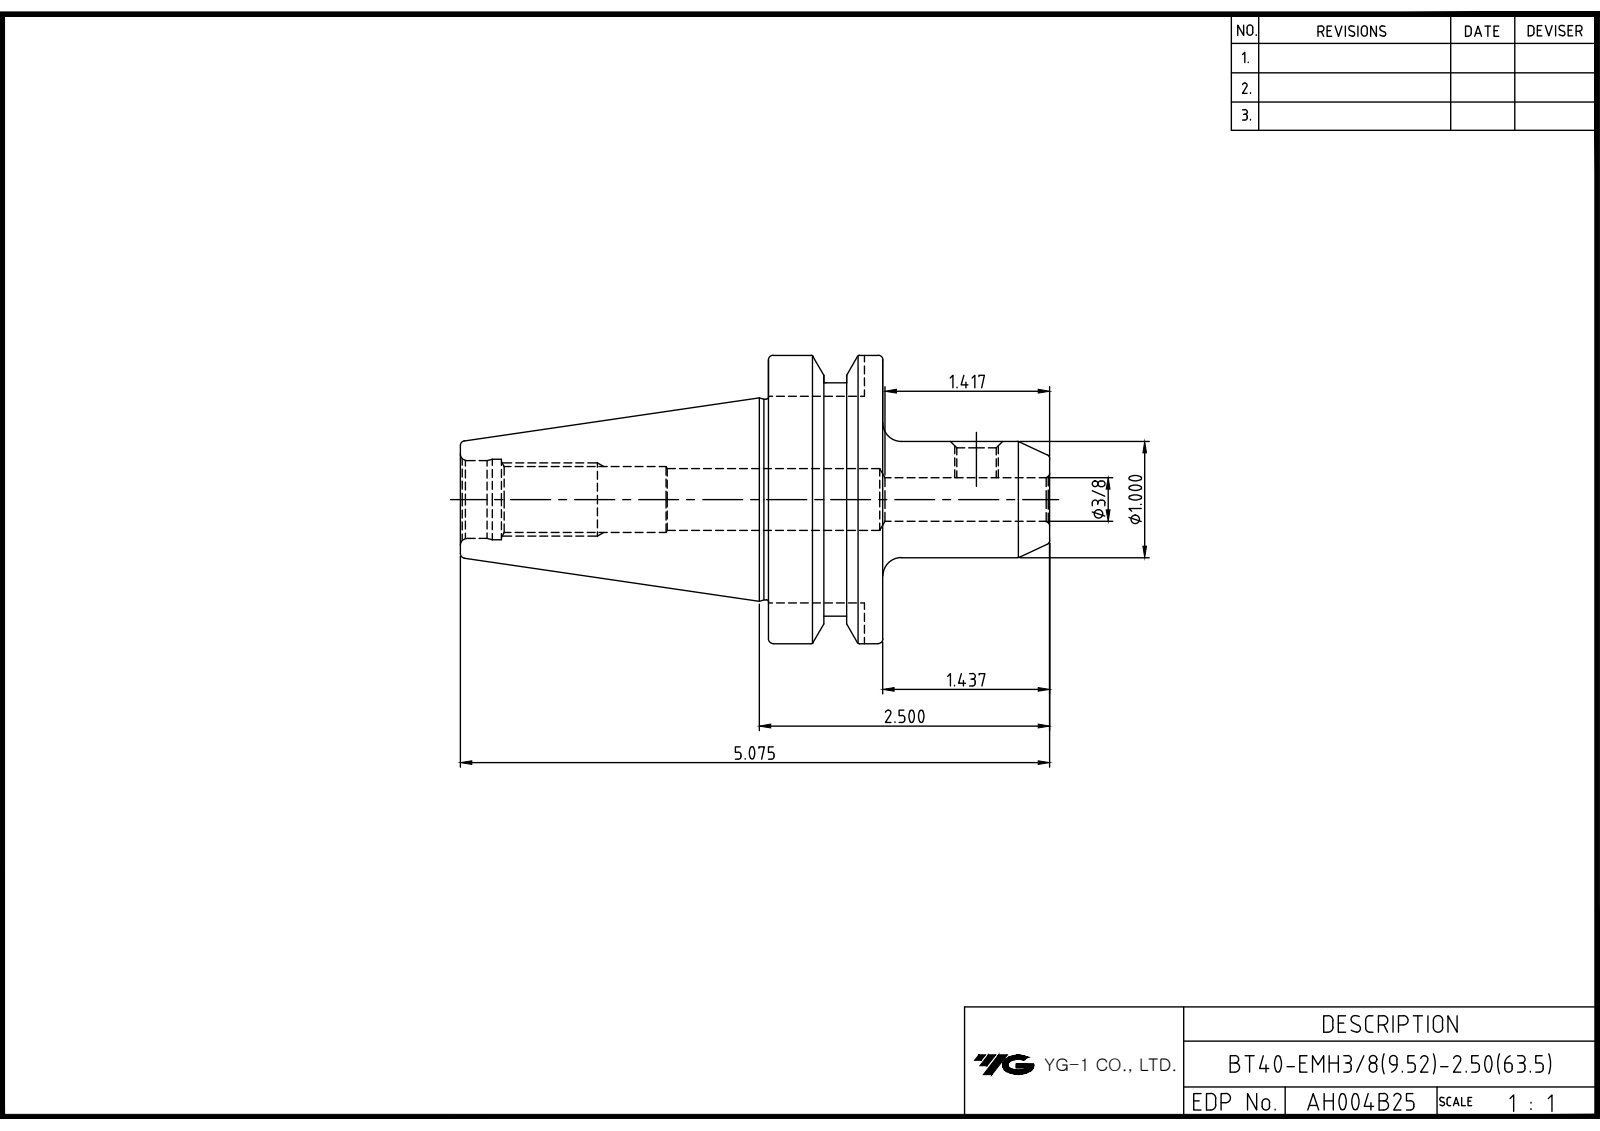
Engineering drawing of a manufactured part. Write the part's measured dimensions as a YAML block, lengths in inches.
part_name: "LO-BT40-EMH9.525-63.5"
step_written_by: "Autodesk Inventor 2022 (AUTOMOTIVE_DESIGN)"
units: inches
bodies: {solids: 1, faces: 49, planar: 15, cylindrical: 15, other: 19}
overall_size: [5.075, 2.48, 2.48]
volume: 8.221
surface_area: 40.69
round_holes:
  - {diameter: 0.33, count: 1}
  - {diameter: 0.375, count: 1}
  - {diameter: 0.531, count: 1}
  - {diameter: 0.545, count: 1}
  - {diameter: 0.669, count: 1}
  - {diameter: 0.693, count: 1}
round_bosses_or_shafts:
  - {diameter: 2.48, count: 1}
  - {diameter: 2.071, count: 1}
  - {diameter: 1.732, count: 1}
  - {diameter: 1, count: 1}
partial_cylinders:
  - {radius: 0.317, count: 1}
face_to_face_distances: [0.984, 1.78, 0.634, 2.421, 1.437, 2.654, 3.638, 5.075, 3.327, 0.673]
